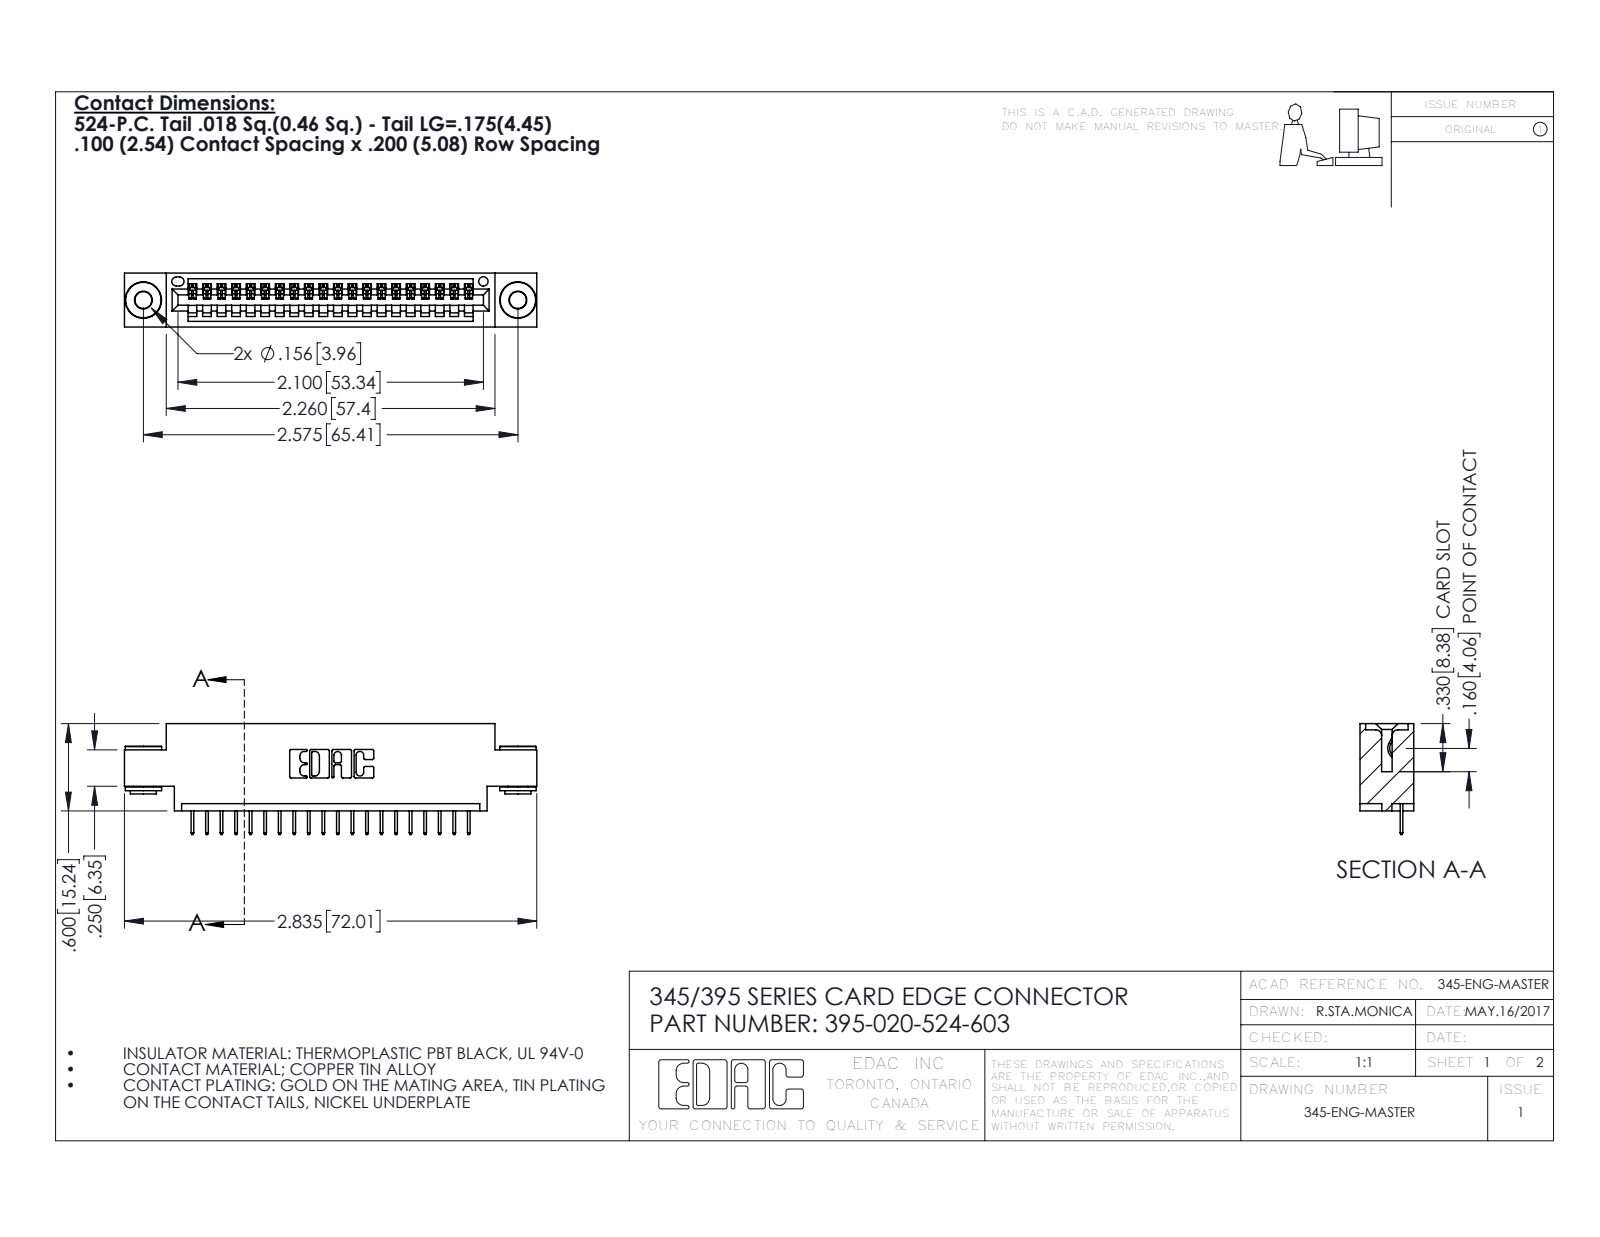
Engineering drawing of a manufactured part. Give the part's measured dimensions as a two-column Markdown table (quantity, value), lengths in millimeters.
| quantity | value |
| --- | --- |
| part name | 345-250-002_345-250-002-102; 395-020-524-603; 345-292-001_345-293-124; 345 Part_0.170 Offset - 0.156 Dia-TH |
| STEP written by | SolidWorks 2016 (CONFIG_CONTROL_DESIGN) |
| units | millimeters |
| bodies | 23 solids, 1408 faces (1014 planar, 386 cylindrical, 8 other) |
| overall size | 72 × 19.4 × 9.4 |
| volume | 6 490 mm³ |
| surface area | 8 406 mm² |
| round holes (diameter × count) | 2.9 × 2, 4 × 2, 1.6 × 1 |
| round bosses / shafts (diameter × count) | 6.4 × 2, 4.6 × 2, 3.5 × 2 |
| partial cylindrical surfaces (radius × count) | 0.2 × 40, 0.3 × 22, 0.2 × 6, 0.8 × 6, 0.7 × 3, 0.8 × 2, 1 × 2, 0.4 × 1 |
| main face-to-face distances | 9.4, 1.8, 7.6, 5.1, 2.5, 6.9, 0.6, 5.7, 4.4, 2.5 |
| hole center spacings | 6.9, 59.5, 65.4 |
